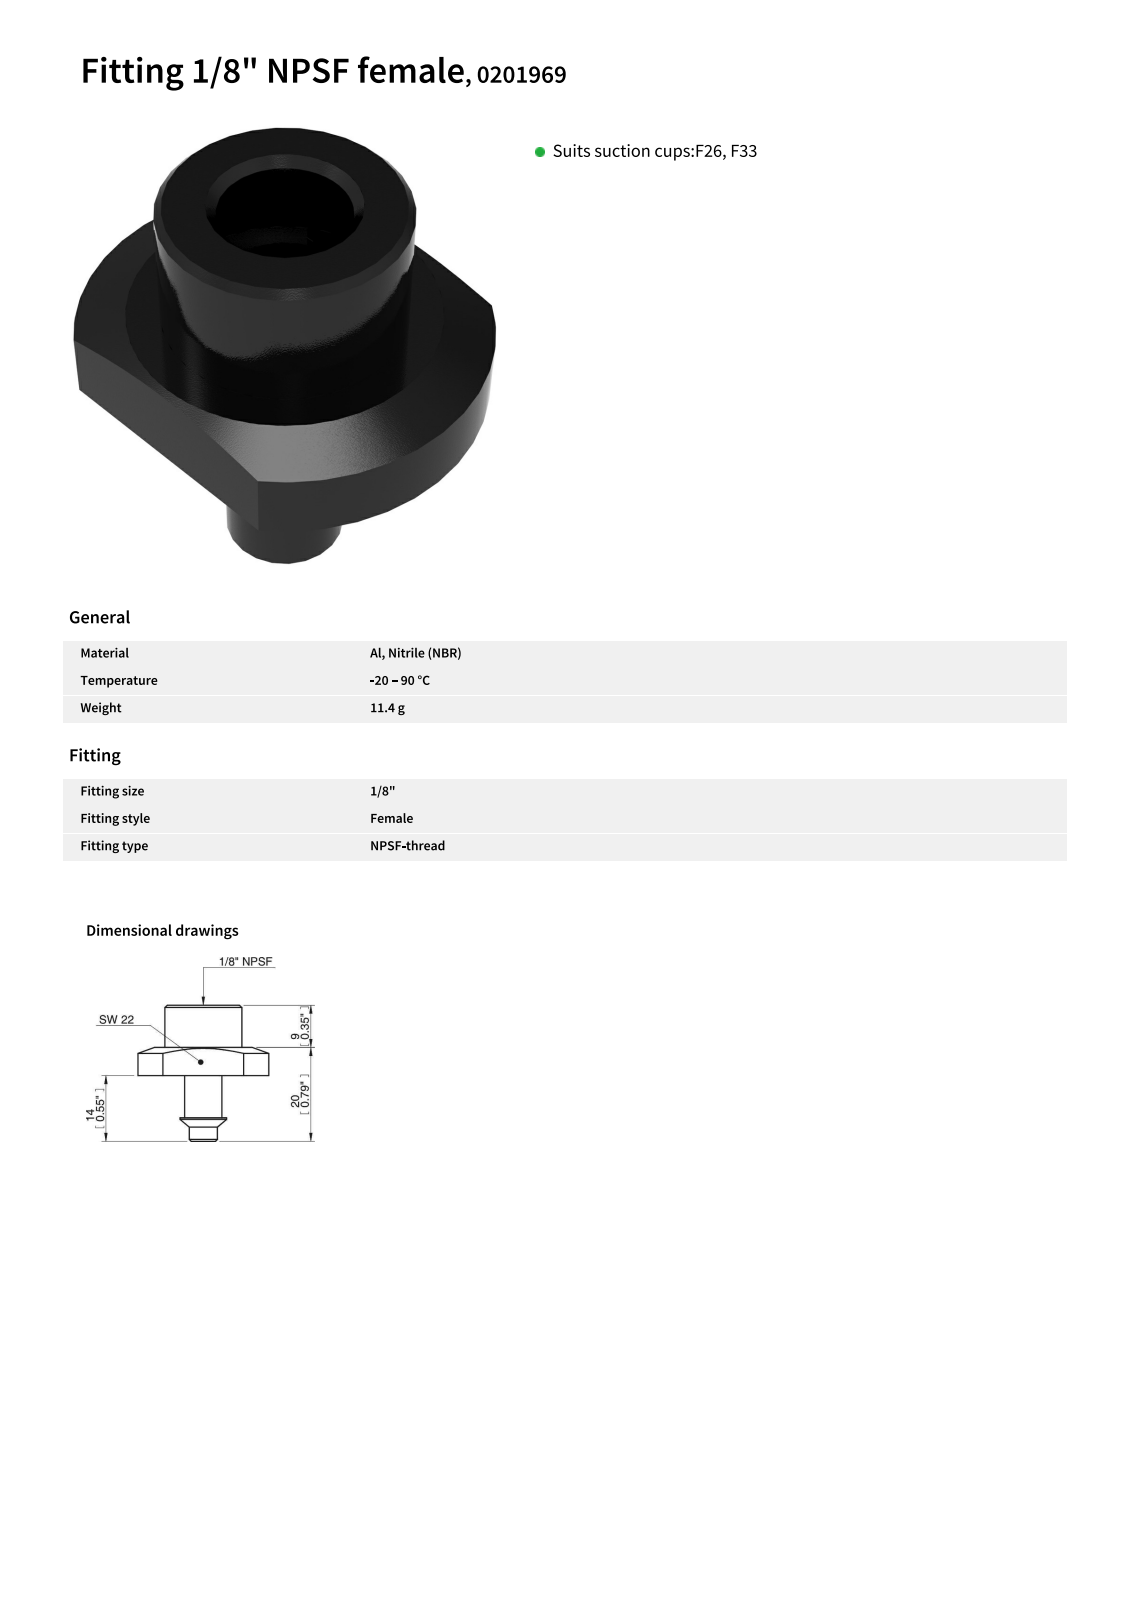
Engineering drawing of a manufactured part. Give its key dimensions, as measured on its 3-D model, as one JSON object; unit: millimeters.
{"step_written_by": "Unknown (AUTOMOTIVE_DESIGN)", "units": "millimeters", "bodies": {"solids": 1, "faces": 22, "planar": 7, "cylindrical": 9, "other": 6}, "overall_size": [29, 28, 22], "volume_mm3": 4743, "surface_area_mm2": 2844, "round_holes": [[4.5, 1], [8.7, 1]], "round_bosses_or_shafts": [[16.5, 1], [10, 1], [8, 1], [6, 1]], "partial_cylinders_radius": [[14, 1]], "face_to_face_distances": [9, 15, 6, 22, 24, 5, 14, 20, 29]}
